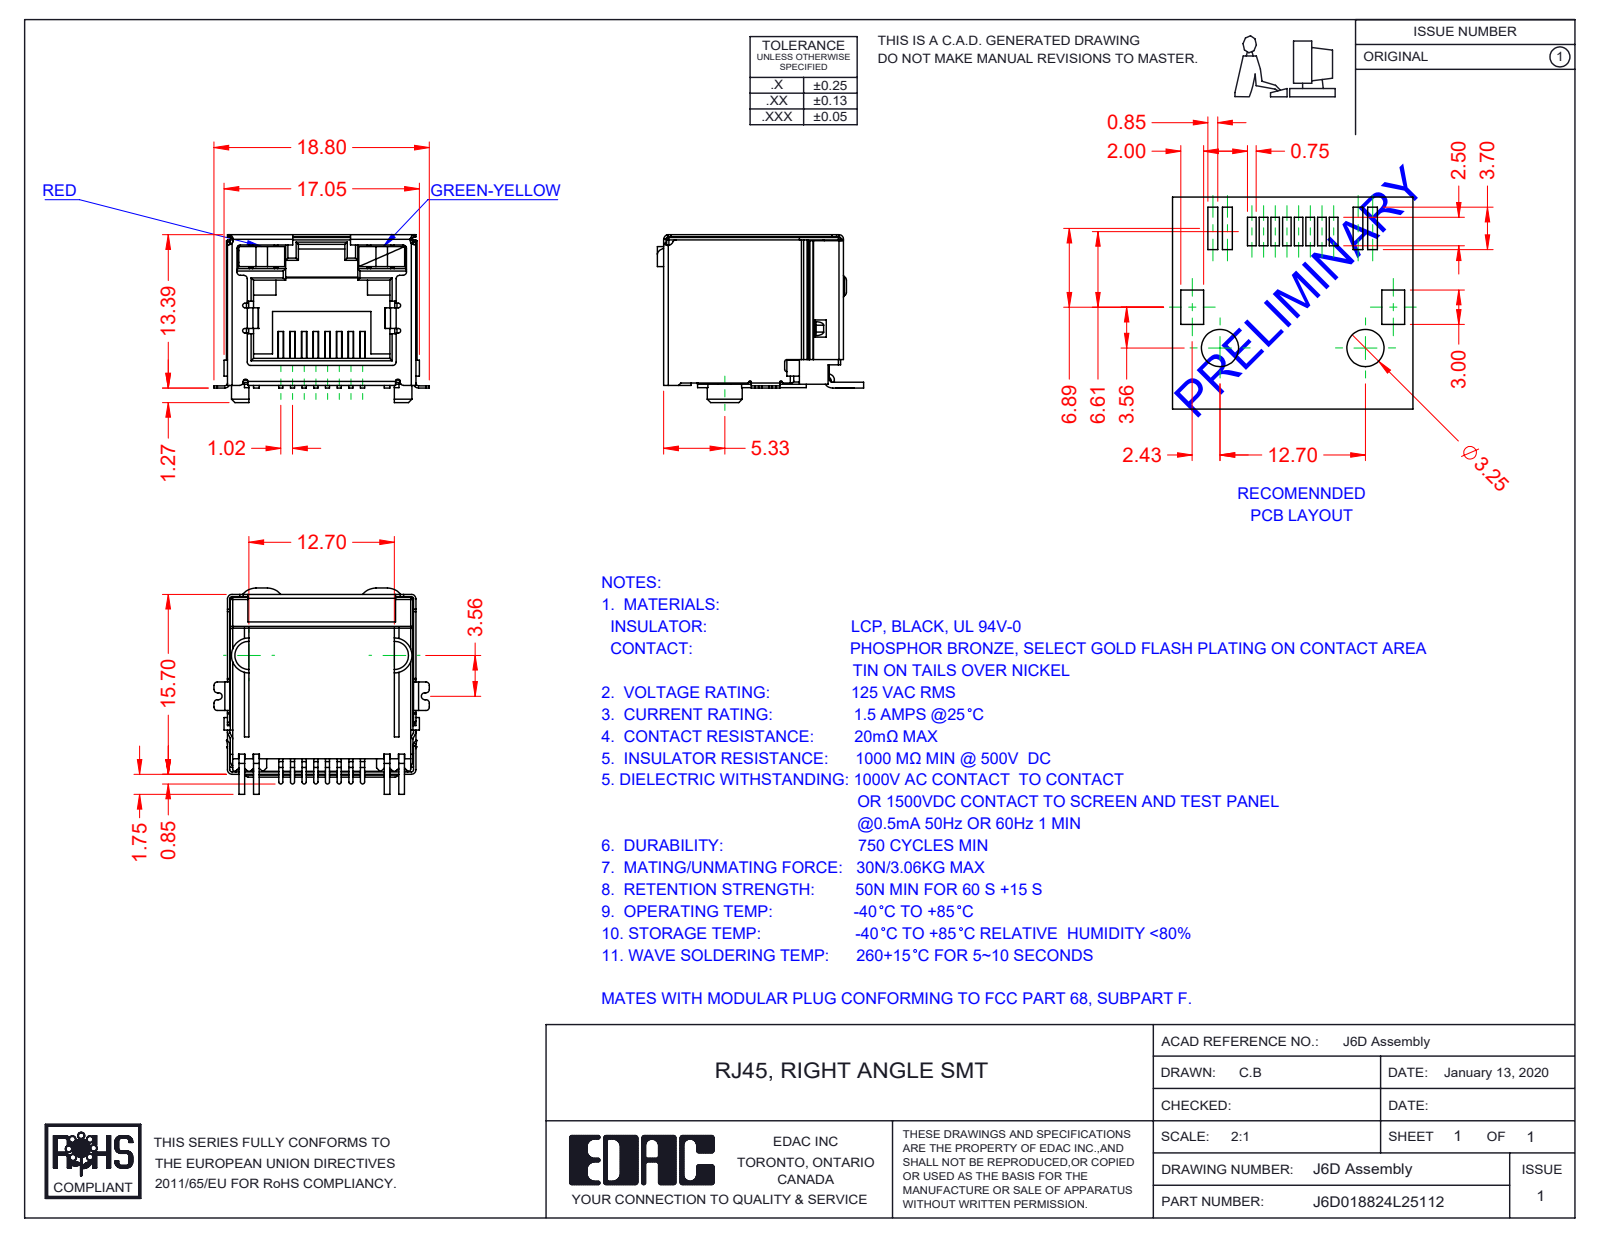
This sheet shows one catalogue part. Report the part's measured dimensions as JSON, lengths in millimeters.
{"part_name": "6D Insulator; 6D LED RH_5-Green-Yellow; J6D018824L25112; 6D Contacts (+2 more)", "step_written_by": "SolidWorks 2016 (CONFIG_CONTROL_DESIGN)", "units": "millimeters", "bodies": {"solids": 12, "faces": 896, "planar": 645, "cylindrical": 218, "other": 33}, "overall_size": [18.8, 18, 14.65], "volume_mm3": 1804, "surface_area_mm2": 4898, "partial_cylinders_radius": [[0.3, 39], [0.2, 37], [0.4, 16], [0.1, 12], [0.15, 8], [0.18, 8], [0.5, 6], [1.5, 5]], "face_to_face_distances": [16, 16.25, 16.2, 2.25, 1, 15.95, 16.05, 12.8, 0.45, 16.45]}
